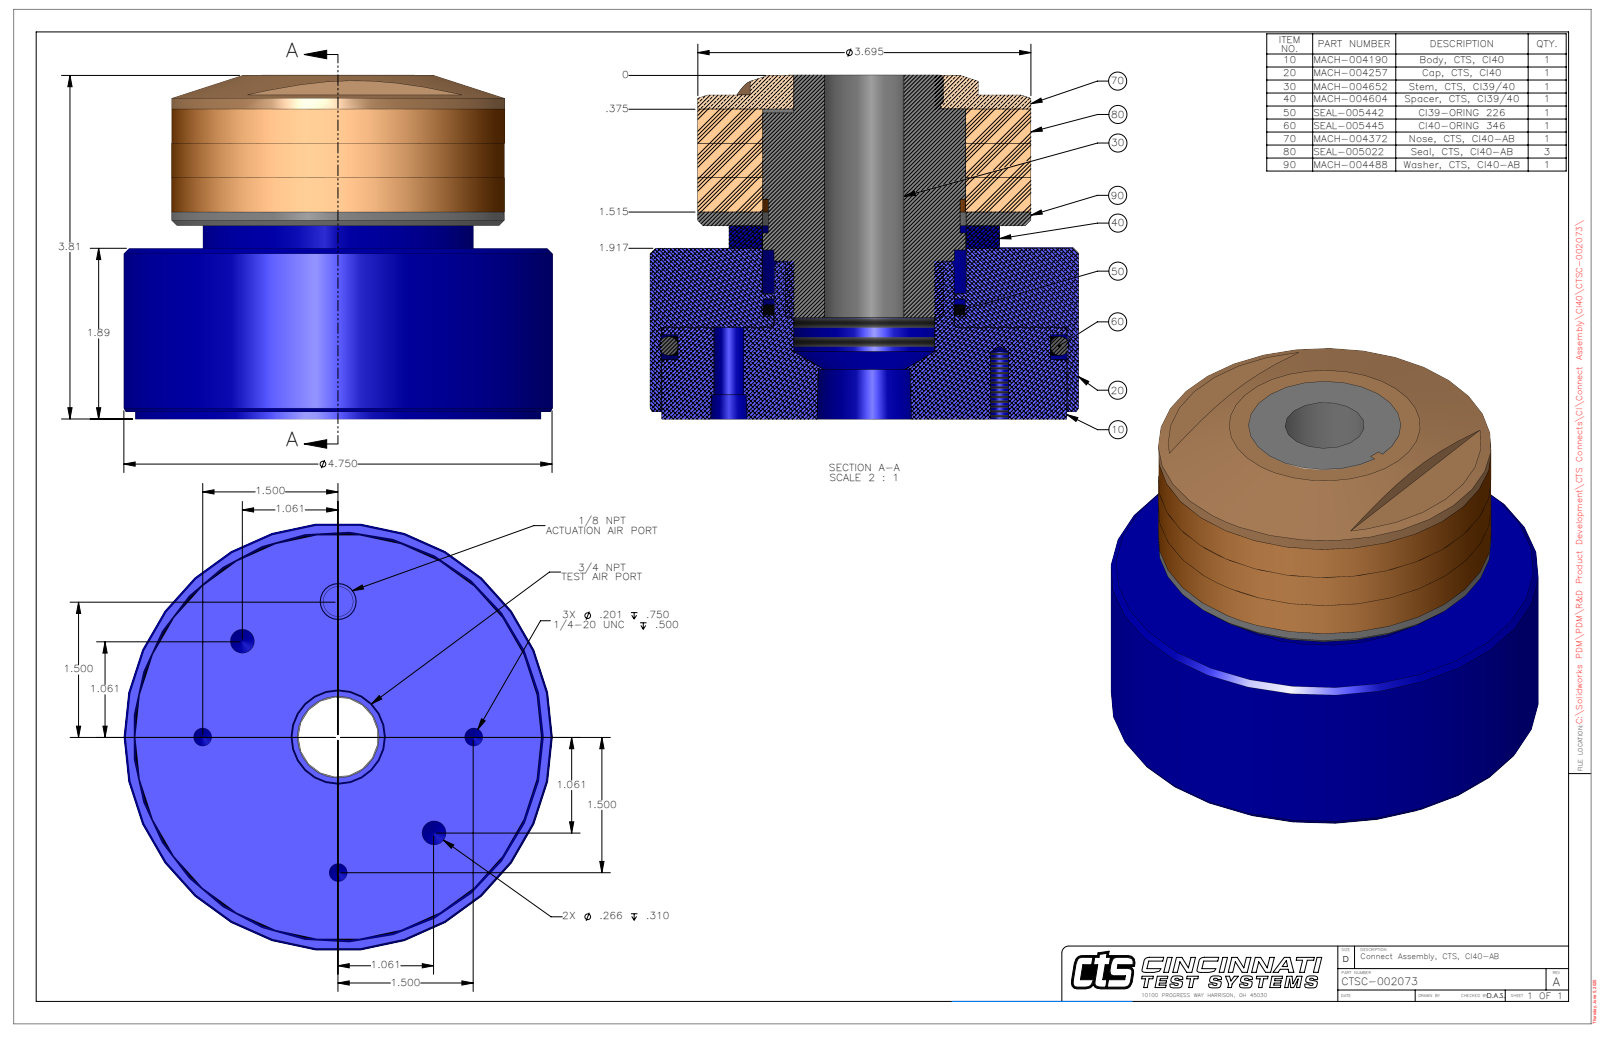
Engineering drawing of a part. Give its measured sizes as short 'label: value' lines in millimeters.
name: CTSC-002073
written by: SolidWorks 2023 (AUTOMOTIVE_DESIGN)
unit: mm
bodies: 1 solid, 94 faces (32 planar, 39 cylindrical, 23 other)
size: 120.7 × 120.7 × 96.9
volume: 806 400 mm³; area: 78 580 mm²
holes: 3× ⌀5.1, 2× ⌀6.8, 1× ⌀8.4, 1× ⌀22.4, 1× ⌀57.2, 1× ⌀57.4, 1× ⌀57.4, 1× ⌀114.3
bosses: 1× ⌀120.7, 1× ⌀114.1, 1× ⌀93.9, 1× ⌀76.2, 1× ⌀53.8
rounds: 1× R1.6, 1× R19.8
face distances: 48.1, 54.4, 6.4, 96.9, 48.8, 42.4, 91.2, 43.1, 36.8, 5.6
hole spacings: 38.1, 29.2, 53.9, 70.4, 76.2
